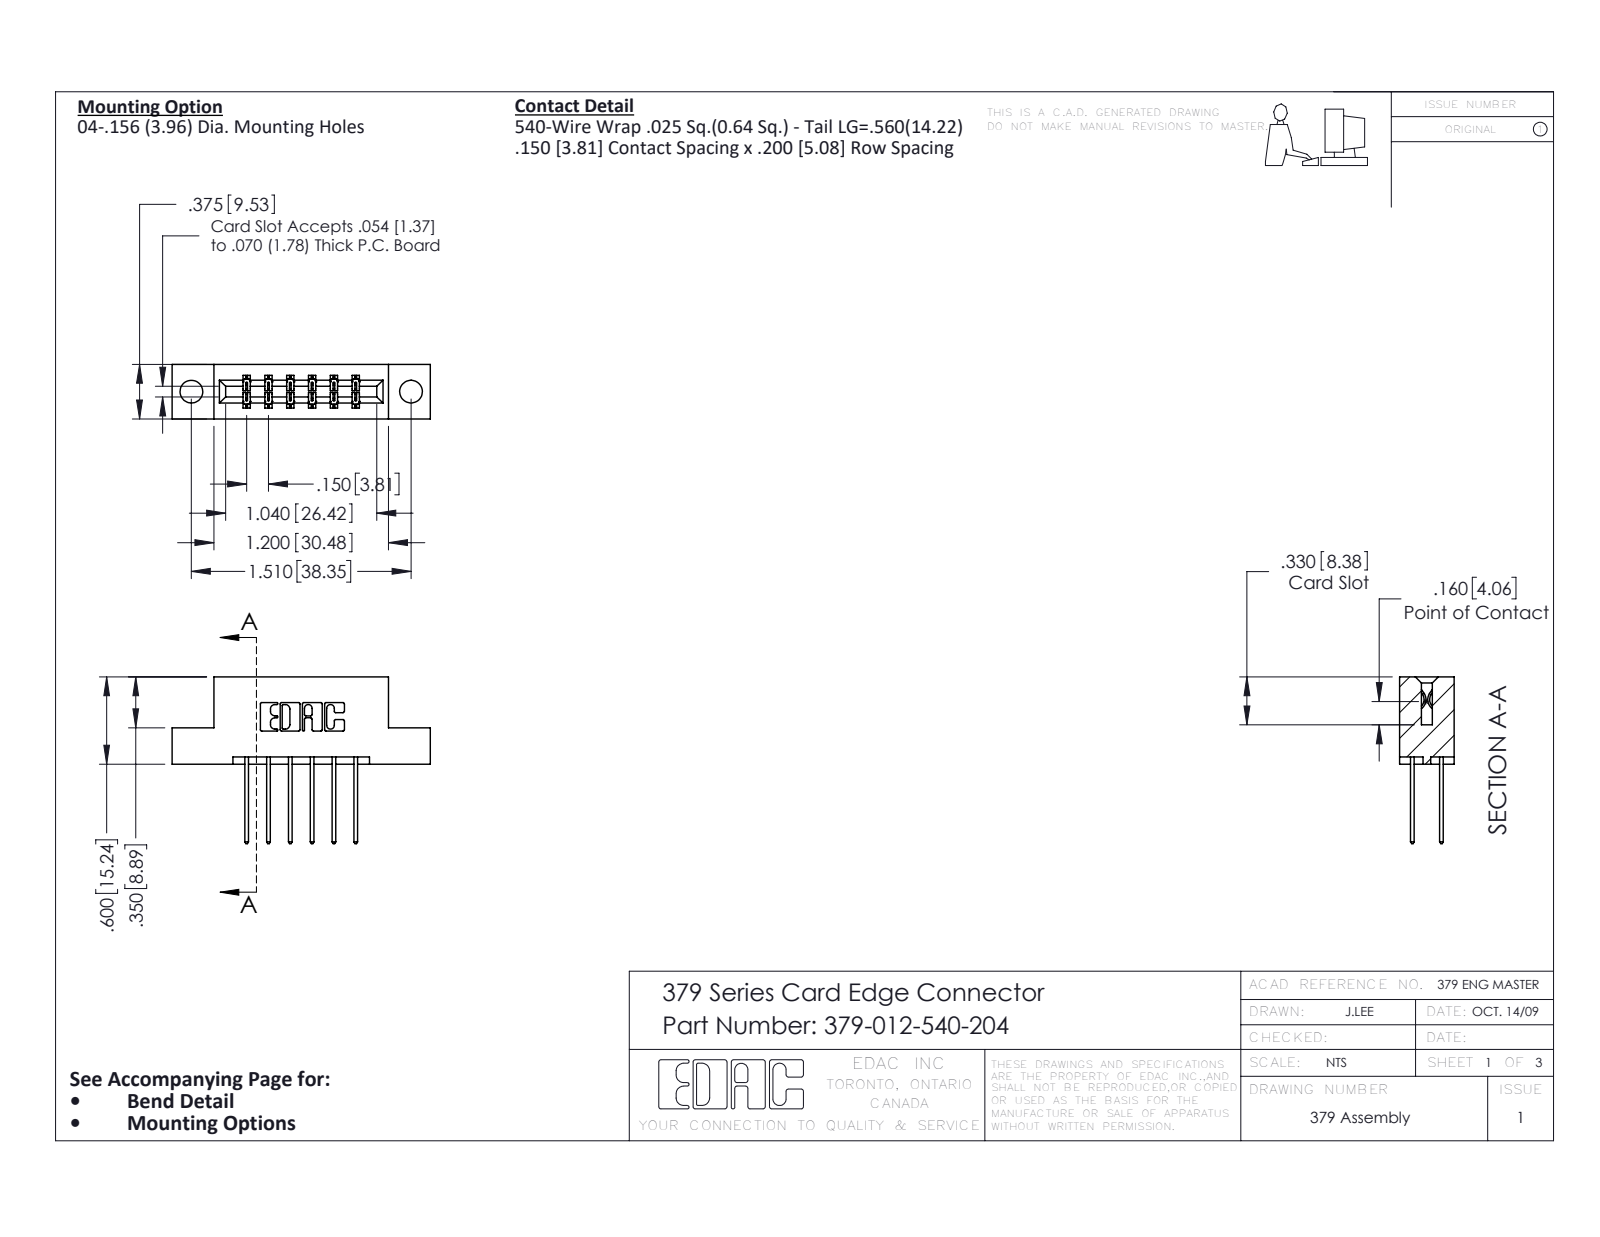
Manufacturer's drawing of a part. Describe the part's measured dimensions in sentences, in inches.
The part is named "379 Part_Flush - .156 Dia - TH; 345-292-001_345-293-140; 379-012-540-204". Its 3-D file was written by "SolidWorks 2016 (CONFIG_CONTROL_DESIGN)". It is 13 solids with 738 faces: 502 planar, 236 cylindrical and 0 other. Overall it measures 1.775 by 1.147 by 0.375 inches. Its volume is 0.263 cubic inches and its surface area 7.016 square inches. Round holes: 2 of diameter 0.156. Partial cylindrical surfaces (rounded edges, fillets, slot ends): 22 of radius 0.01, 18 of radius 0.006, 12 of radius 0.01, 6 of radius 0.007, 6 of radius 0.031, 3 of radius 0.026, 2 of radius 0.014, 2 of radius 0.022. The main face-to-face distances are 0.3, 0.2, 0.15, 0.1, 0.375, 0.05, 0.075, 0.25, 0.35, 0.55. The hole center spacings are 1.51.
